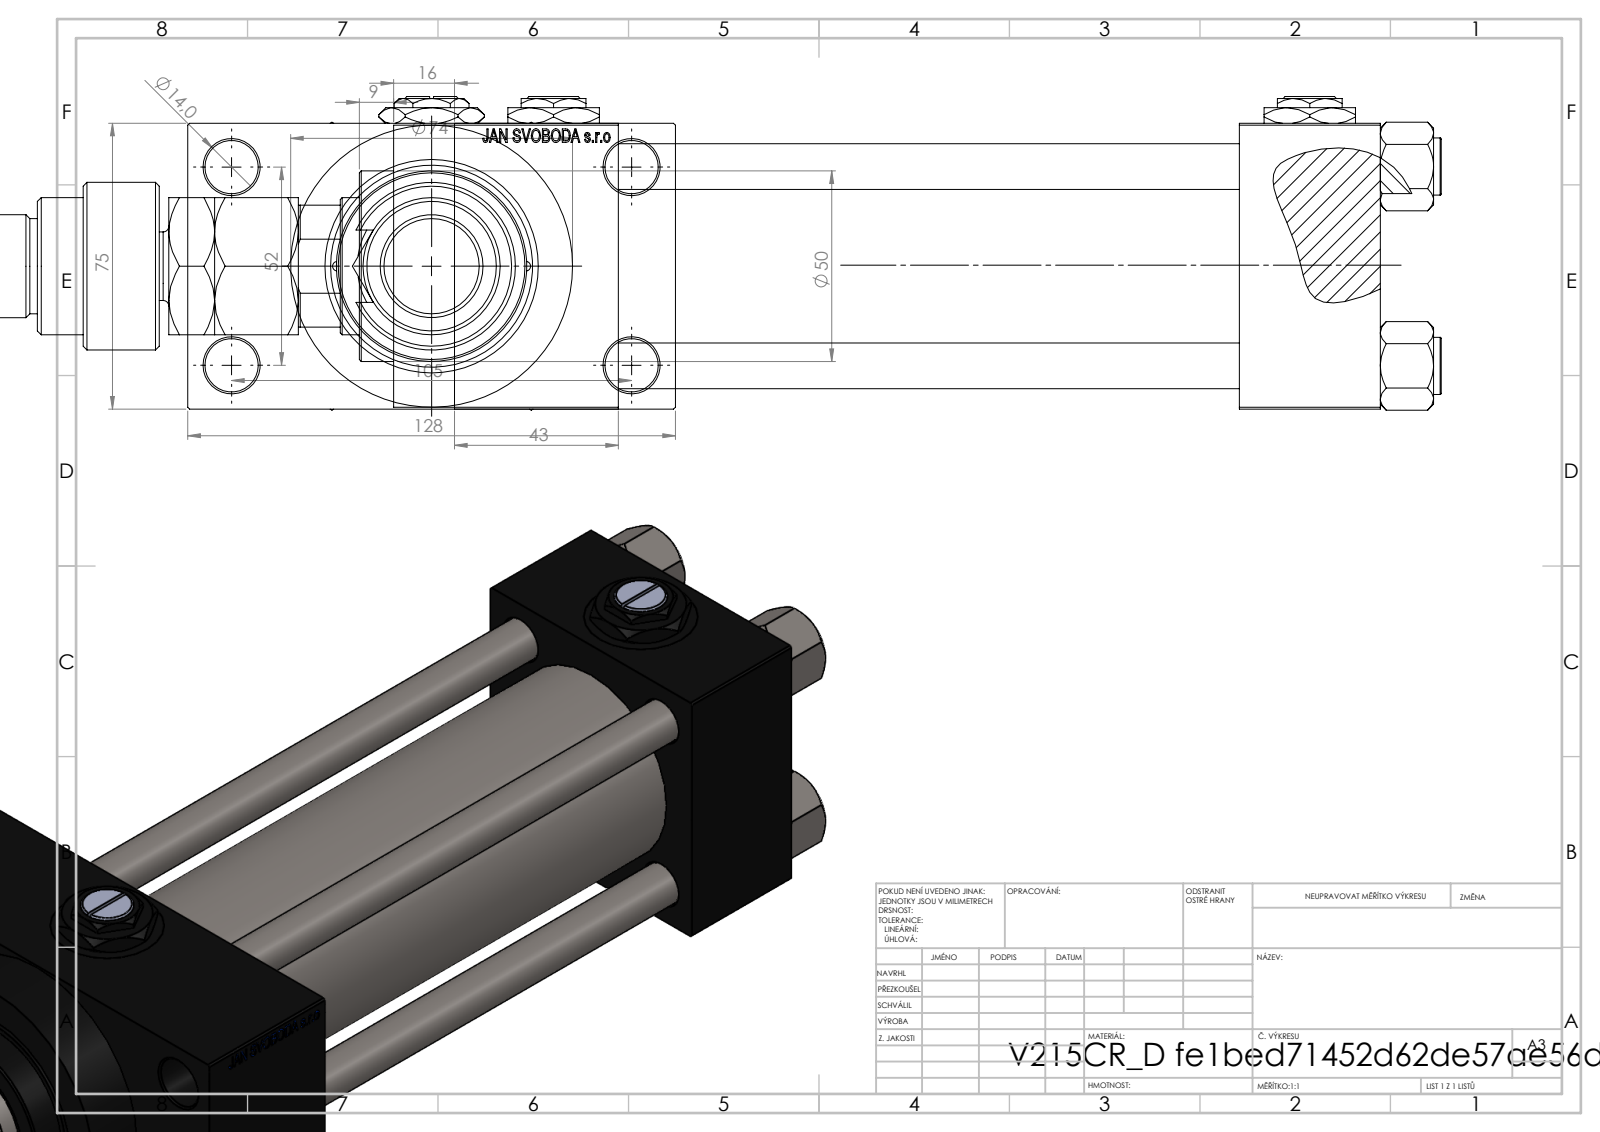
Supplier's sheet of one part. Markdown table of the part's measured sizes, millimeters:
| quantity | value |
| --- | --- |
| part name | FEMALE_PART_FOR_DFA; V215CR_VCP_D; V215CR_D_Body; MFA (+4 more) |
| STEP written by | SolidWorks 2019 (CONFIG_CONTROL_DESIGN) |
| units | millimeters |
| bodies | 15 solids, 1299 faces (577 planar, 116 cylindrical, 606 other) |
| overall size | 410.5 × 128 × 82.27 |
| volume | 1 118 000 mm³ |
| surface area | 263 507 mm² |
| round holes (diameter × count) | 12 × 4, 14 × 4, 20.96 × 4, 30 × 4, 7 × 3, 2.5 × 2, 25.5 × 1, 39 × 1, 41 × 1, 53 × 1 |
| round bosses / shafts (diameter × count) | 15 × 4, 74 × 1, 56 × 1, 50 × 1, 44 × 1, 36 × 1, 28 × 1, 27 × 1 |
| partial cylindrical surfaces (radius × count) | 9.5 × 1, 15 × 1, 17.5 × 1 |
| main face-to-face distances | 75, 163, 37, 200, 26.5, 243, 43, 206, 101.5, 59 |
| hole center spacings | 26.19, 26.35, 36.98, 38.03, 52.3, 57.22, 58.43, 58.59 |
